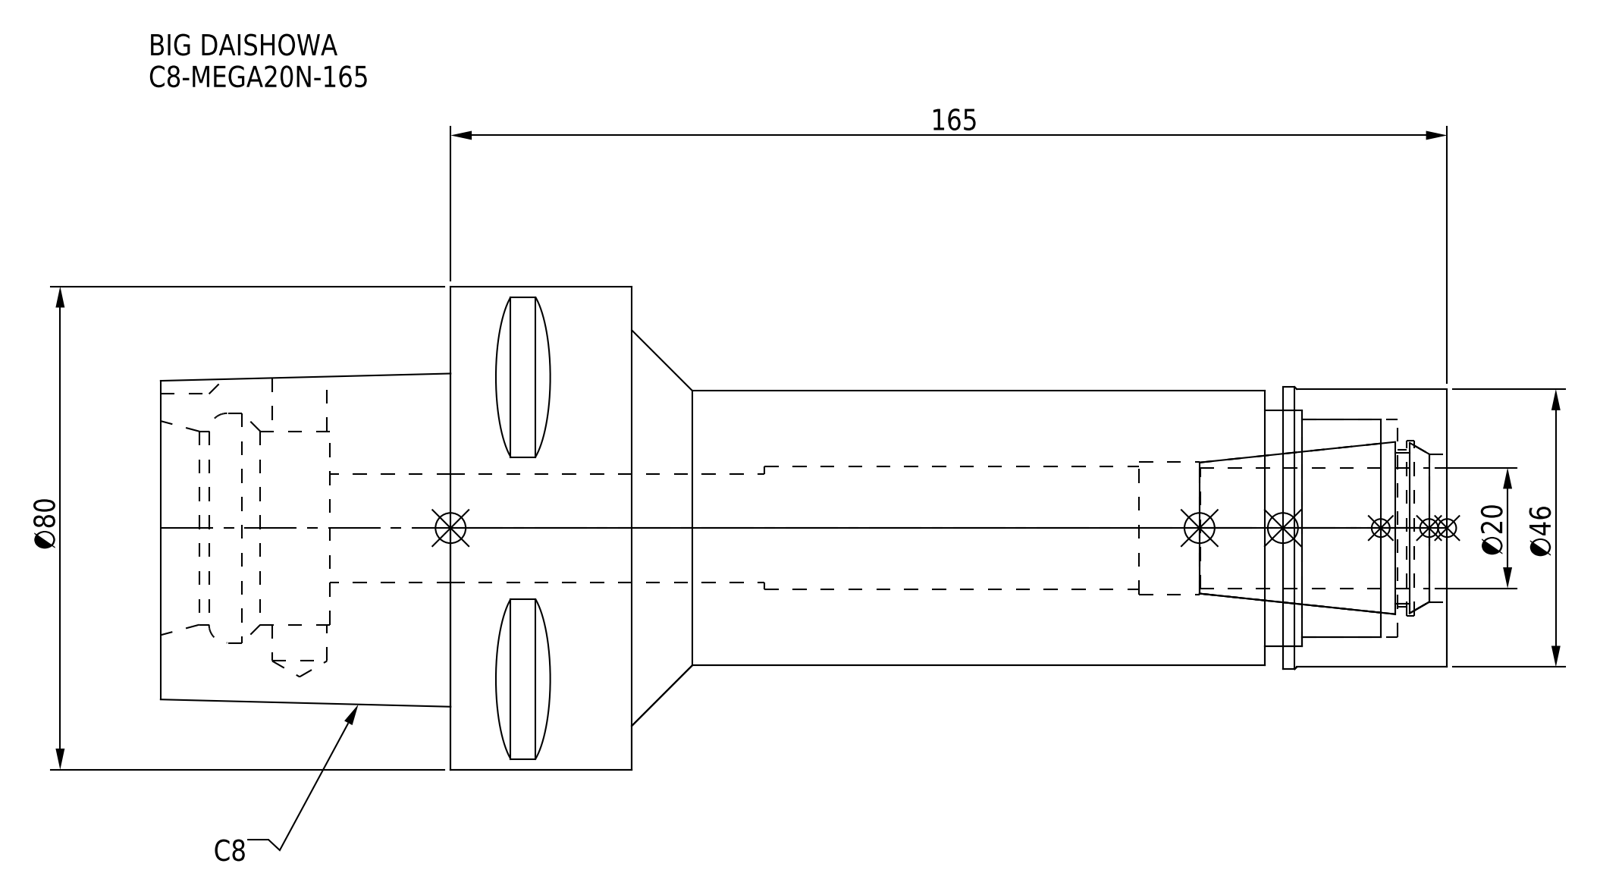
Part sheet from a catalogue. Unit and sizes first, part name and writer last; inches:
Units: inches
Overall size (bounding box): 8.386 × 3.15 × 3.15
Round holes (diameter × count): ⌀0.358 ×1, ⌀0.709 ×1, ⌀0.799 ×1, ⌀0.866 ×1, ⌀0.965 ×1, ⌀1.024 ×1, ⌀1.142 ×1, ⌀1.26 ×1, ⌀1.417 ×1, ⌀1.496 ×1, ⌀1.535 ×1
Round bosses / shafts (diameter × count): ⌀3.15 ×1, ⌀1.839 ×1, ⌀1.811 ×1, ⌀1.791 ×1
Partial cylindrical surfaces — rounded edges, fillets, slot ends (radius × count): R0.236 ×1
Main face-to-face distances: 1.181, 5.315, 6.496, 8.386, 3.071, 1.89, 0.787, 7.283, 1.969, 1.102
Volume: 24.02 in³ · Surface area: 101.9 in²
Bodies: 2 solids, 95 faces (38 planar, 39 cylindrical, 18 other)
Part name (STEP PRODUCT): C8-MEGA20N-165-200.stp; C8-MEGA20N-165_1.stp; C8-MEGA20N-165-200-FreeParts; C8-MEGA20N-165-200_ASM.stp (+3 more)
STEP written by: SolidWorks 2019 (CONFIG_CONTROL_DESIGN)
